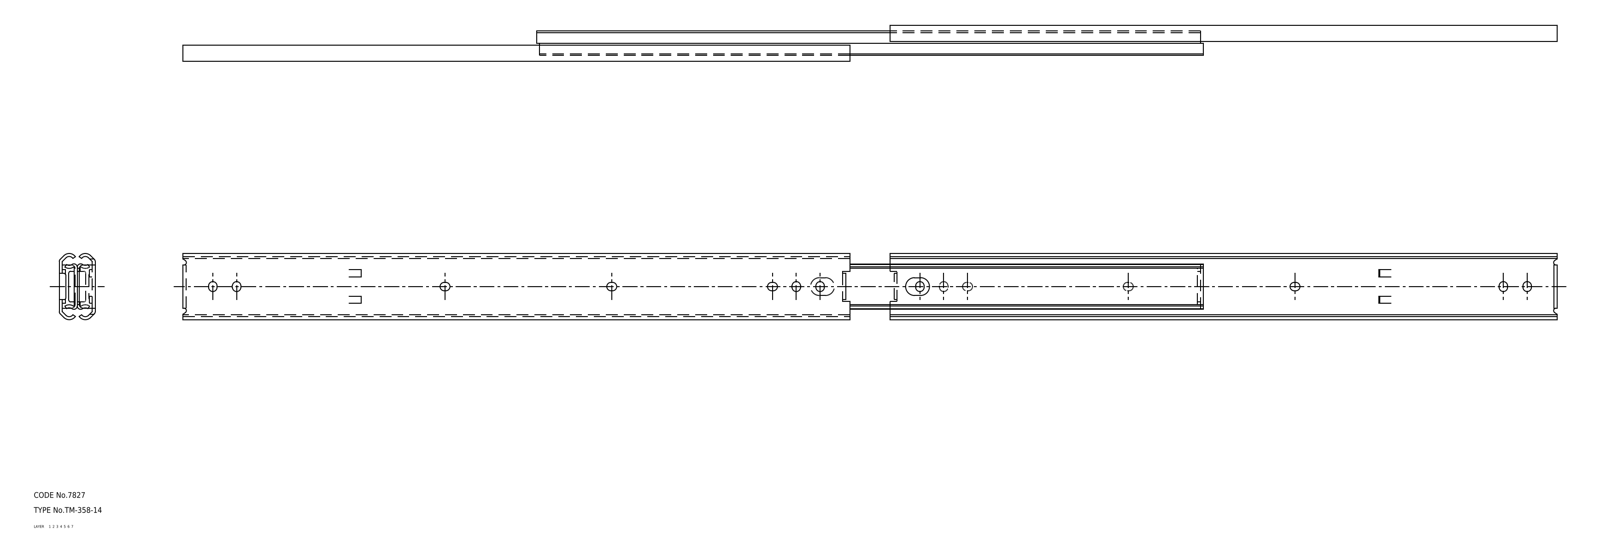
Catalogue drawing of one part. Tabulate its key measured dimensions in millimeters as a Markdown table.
| quantity | value |
| --- | --- |
| part name | member_B; member_A1^TM_358_14; TM_358_14 |
| STEP written by | SolidWorks 2015 (AUTOMOTIVE_DESIGN) |
| units | millimeters |
| bodies | 3 solids, 212 faces (122 planar, 90 cylindrical, 0 other) |
| overall size | 732.6 × 35.3 × 19.2 |
| volume | 88 244 mm³ |
| surface area | 101 916 mm² |
| partial cylindrical surfaces (radius × count) | 2.25 × 28, 1.6 × 10, 1 × 8, 2.4 × 8, 4 × 8, 0.2 × 4, 1.3 × 4, 1.8 × 4 |
| main face-to-face distances | 1.6, 17.6, 8, 9.6, 11.2, 6.4, 16, 19.2, 3.2, 31.8 |
